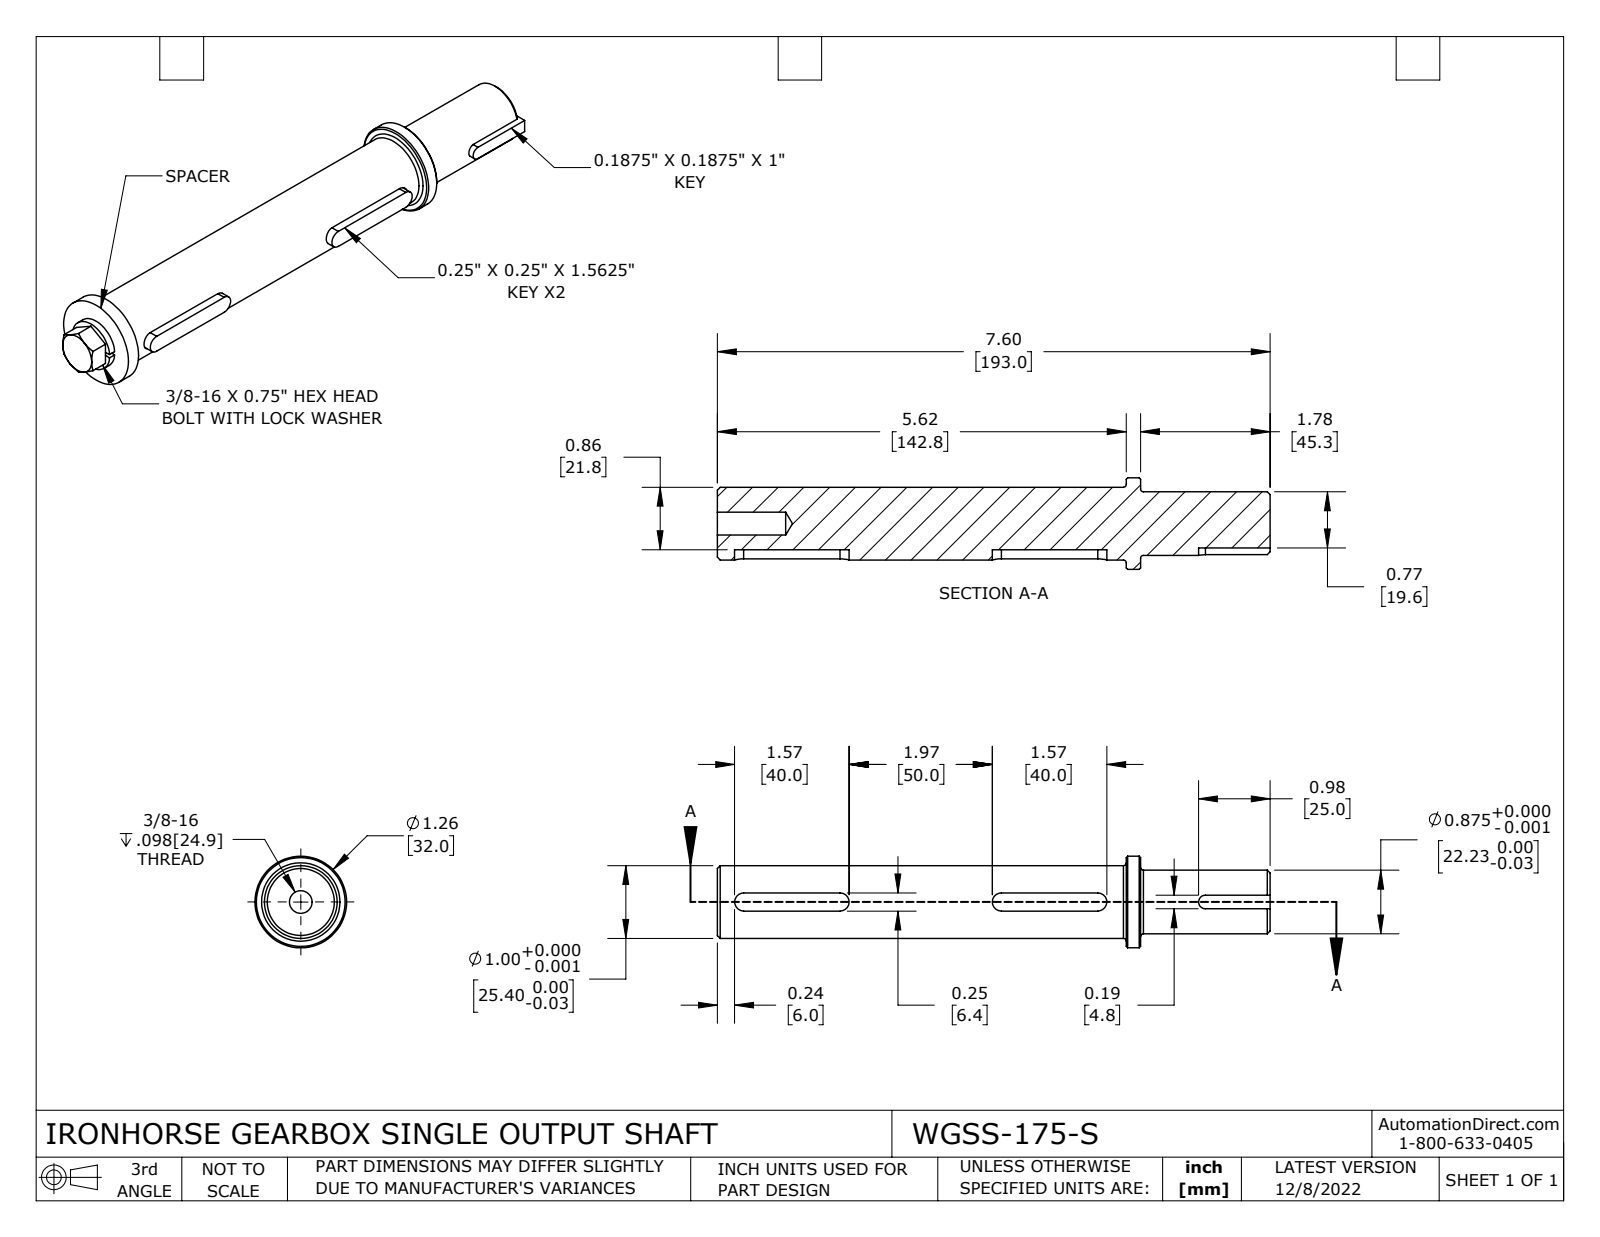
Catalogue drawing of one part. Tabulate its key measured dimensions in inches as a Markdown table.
| quantity | value |
| --- | --- |
| part name | WGSS-175-S |
| STEP written by | SolidWorks 2021 (CONFIG_CONTROL_DESIGN) |
| units | inches |
| bodies | 7 solids, 92 faces (41 planar, 28 cylindrical, 23 other) |
| overall size | 8.179 × 1.26 × 1.26 |
| volume | 6.159 in³ |
| surface area | 37.6 in² |
| round holes (diameter × count) | 0.313 × 1, 0.394 × 1, 0.402 × 1 |
| round bosses / shafts (diameter × count) | 1.26 × 1, 1 × 1, 0.875 × 1, 0.724 × 1, 0.375 × 1 |
| partial cylindrical surfaces (radius × count) | 0.125 × 6, 0.094 × 1 |
| main face-to-face distances | 0.197, 0.25, 5.818, 0.25, 0.031, 0.219, 7.796, 7.6, 6.015, 1.781 |
